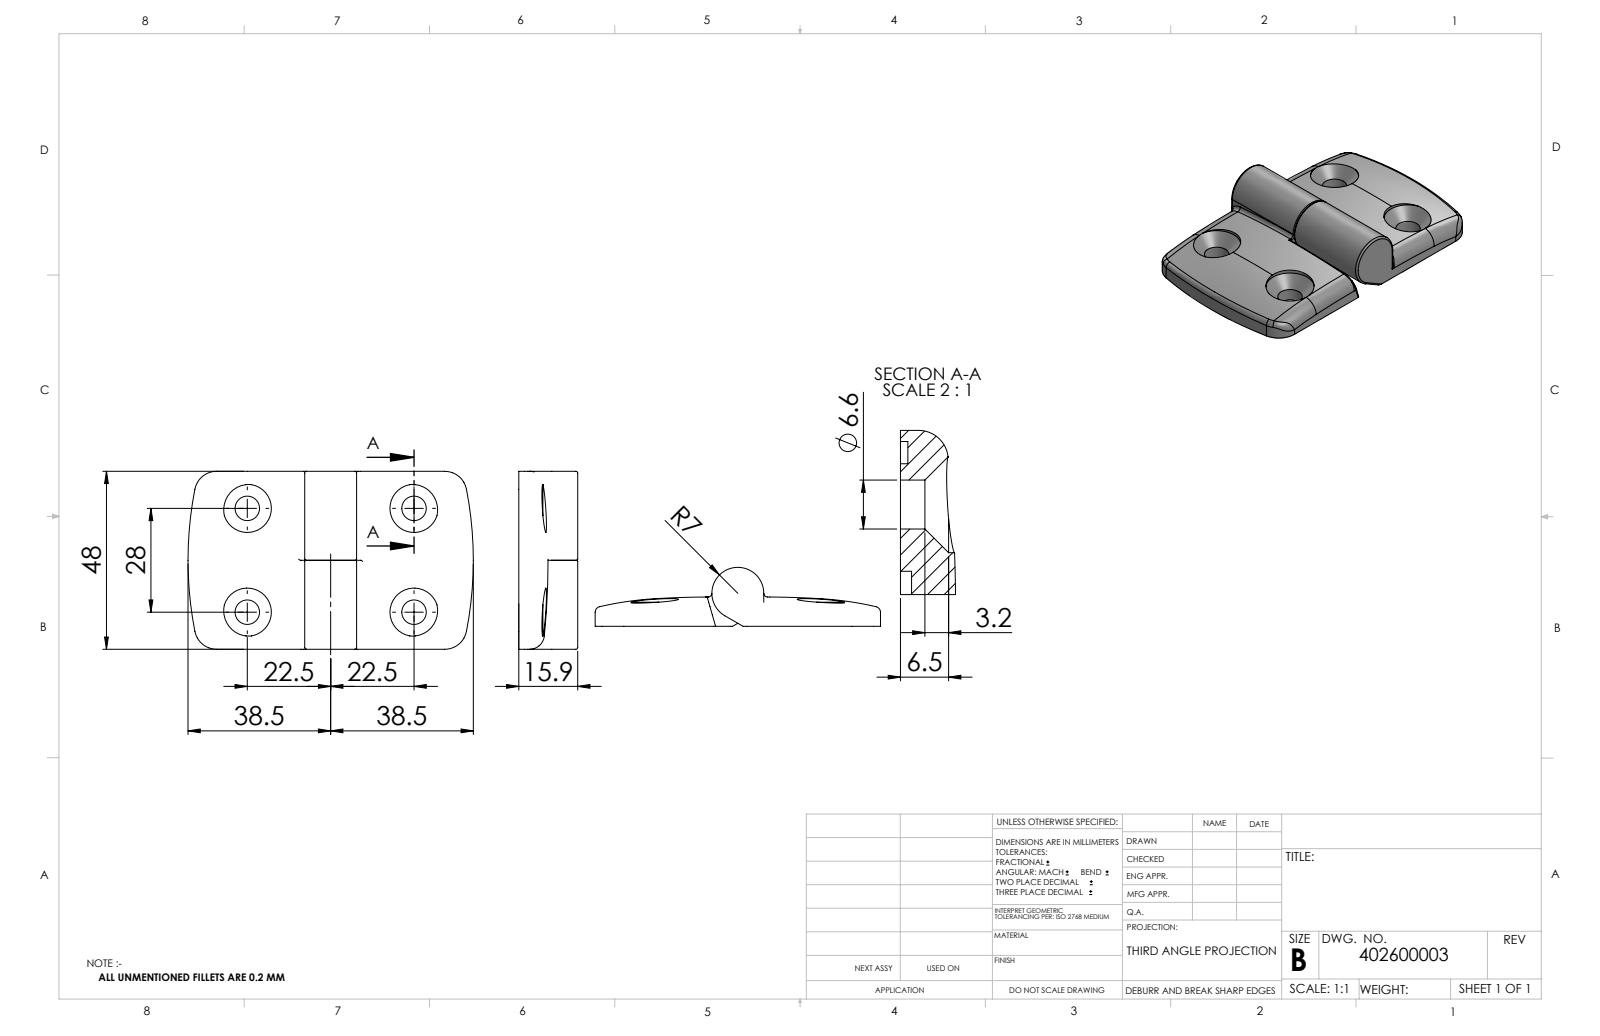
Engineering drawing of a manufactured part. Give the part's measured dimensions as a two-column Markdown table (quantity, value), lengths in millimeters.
| quantity | value |
| --- | --- |
| part name | 402600003_c_1 |
| STEP written by | SolidWorks 2014 (CONFIG_CONTROL_DESIGN) |
| units | millimeters |
| bodies | 3 solids, 171 faces (68 planar, 43 cylindrical, 60 other) |
| overall size | 77 × 48 × 15.9 |
| volume | 24 676 mm³ |
| surface area | 12 459 mm² |
| round holes (diameter × count) | 6.6 × 4, 6 × 1 |
| round bosses / shafts (diameter × count) | 14 × 1 |
| partial cylindrical surfaces (radius × count) | 0.5 × 6, 0.3 × 4, 6 × 4, 6.5 × 4, 4 × 2, 100 × 2 |
| main face-to-face distances | 1.5, 24, 5, 3, 48, 2, 0.5, 19, 29, 1 |
| hole center spacings | 28, 45, 53 |
